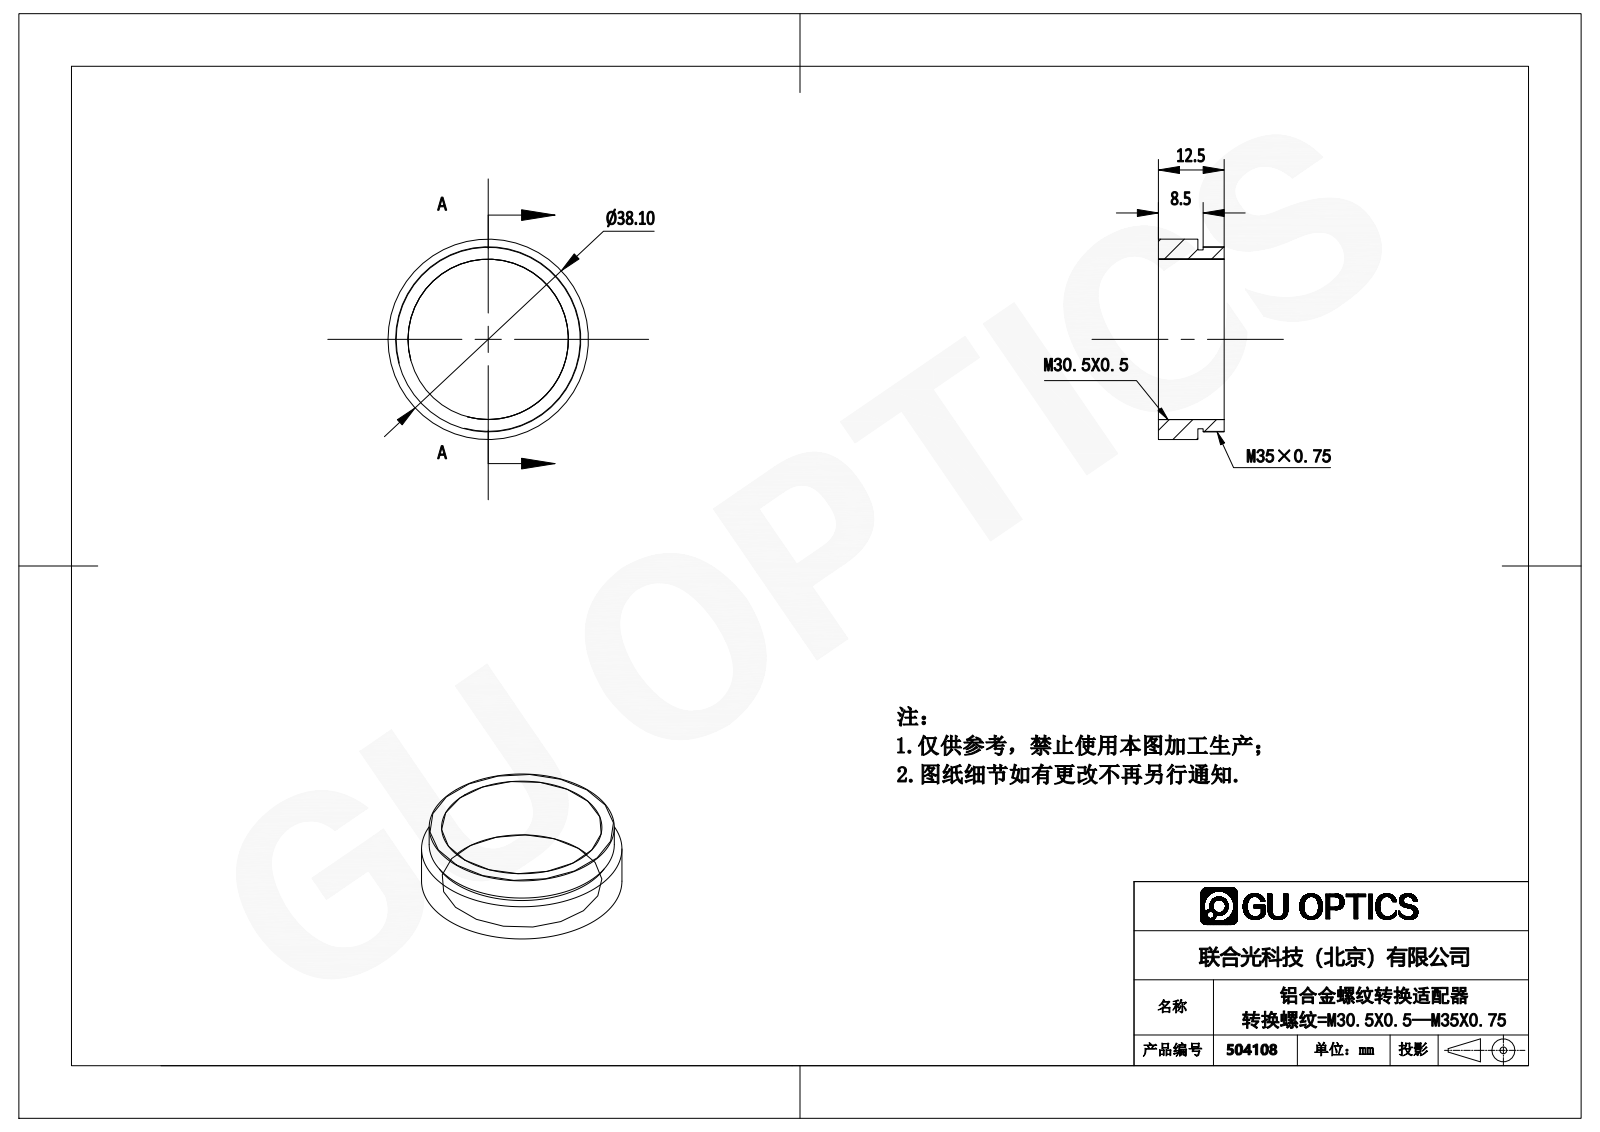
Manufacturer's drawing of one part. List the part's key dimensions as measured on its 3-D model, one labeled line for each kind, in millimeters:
Part name (STEP PRODUCT): 504108
STEP written by: SolidWorks 2016 (AUTOMOTIVE_DESIGN)
Units: millimetres
Bodies: 1 solid, 12 faces (4 planar, 8 cylindrical, 0 other)
Overall size (bounding box): 38.1 × 38.1 × 12.5
Volume: 4 230 mm³ · Surface area: 3 595 mm²
Round holes (diameter × count): ⌀30.48 ×1
Round bosses / shafts (diameter × count): ⌀38.1 ×1, ⌀35.2 ×1, ⌀34 ×1
Main face-to-face distances: 12.5, 7.5, 5, 8.5, 1, 4
